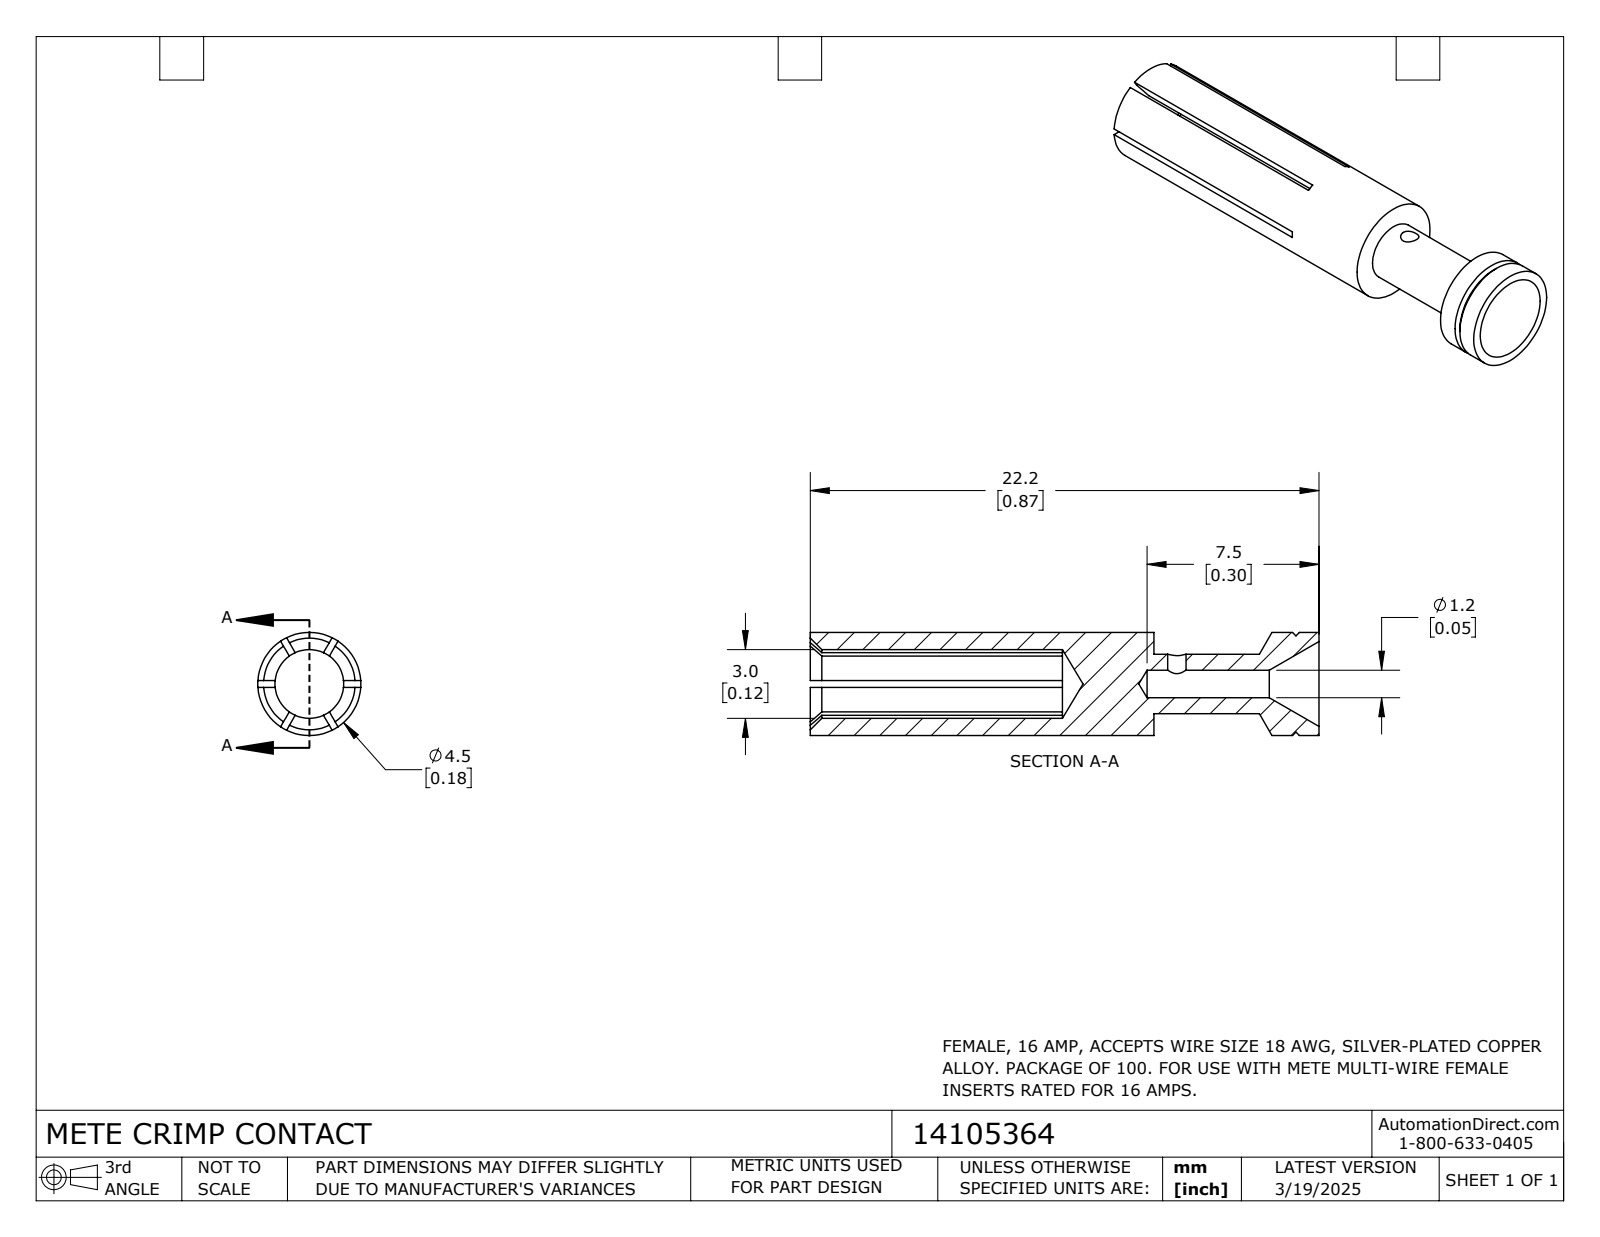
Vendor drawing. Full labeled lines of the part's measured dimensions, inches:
Part name (STEP PRODUCT): 14105364
STEP written by: SolidWorks 2024 (CONFIG_CONTROL_DESIGN)
Units: inches
Bodies: 1 solid, 62 faces (26 planar, 18 cylindrical, 18 other)
Overall size (bounding box): 0.874 × 0.177 × 0.177
Volume: 0.011 in³ · Surface area: 0.817 in²
Round holes (diameter × count): ⌀0.031 ×1, ⌀0.047 ×1, ⌀0.118 ×1
Round bosses / shafts (diameter × count): ⌀0.177 ×1, ⌀0.102 ×1
Main face-to-face distances: 0.283, 0.874, 0.591, 0.441, 0.157, 0.433
